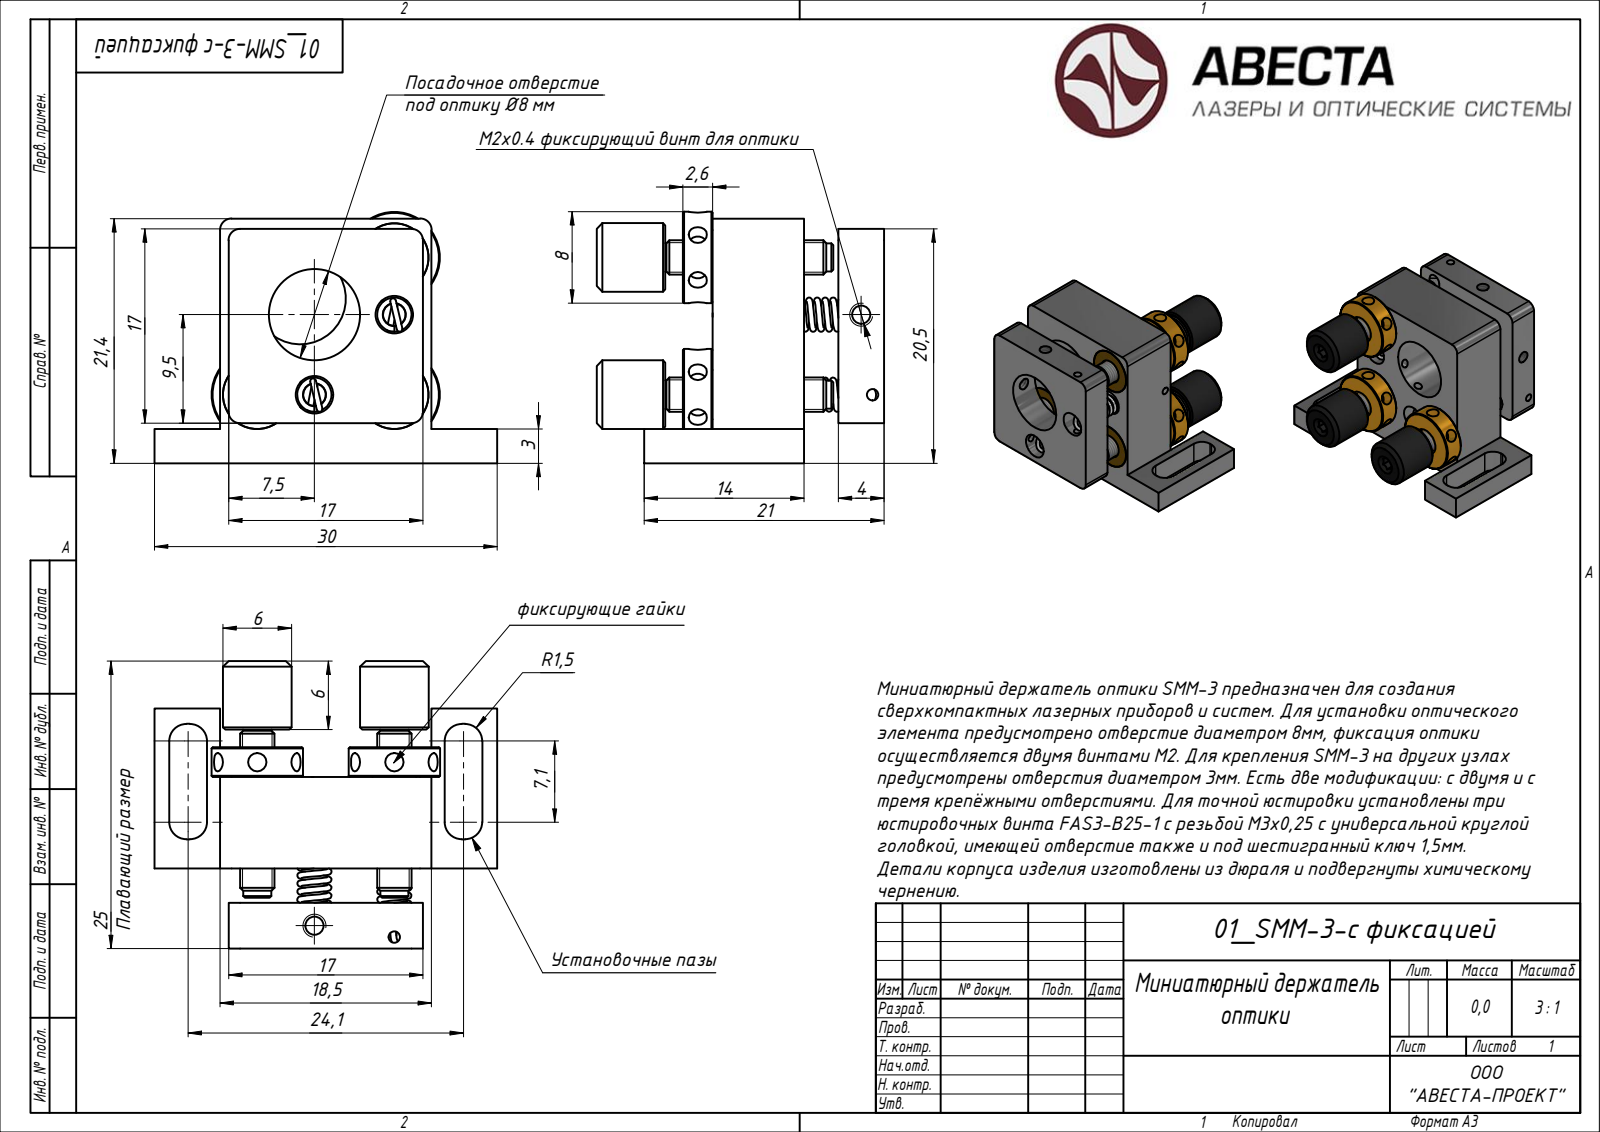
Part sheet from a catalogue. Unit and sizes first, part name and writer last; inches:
Units: inches
Overall size (bounding box): 1.181 × 0.99 × 0.866
Main face-to-face distances: 0.315, 0.118, 0.157, 0.591, 0.276, 0.433, 0.728, 0.843, 0.236, 0.03
Volume: 0.287 in³ · Surface area: 10.33 in²
Bodies: 19 solids, 433 faces (86 planar, 0 cylindrical, 347 other)
STEP written by: ST-DEVELOPER v15 (AUTOMOTIVE_DESIGN)
